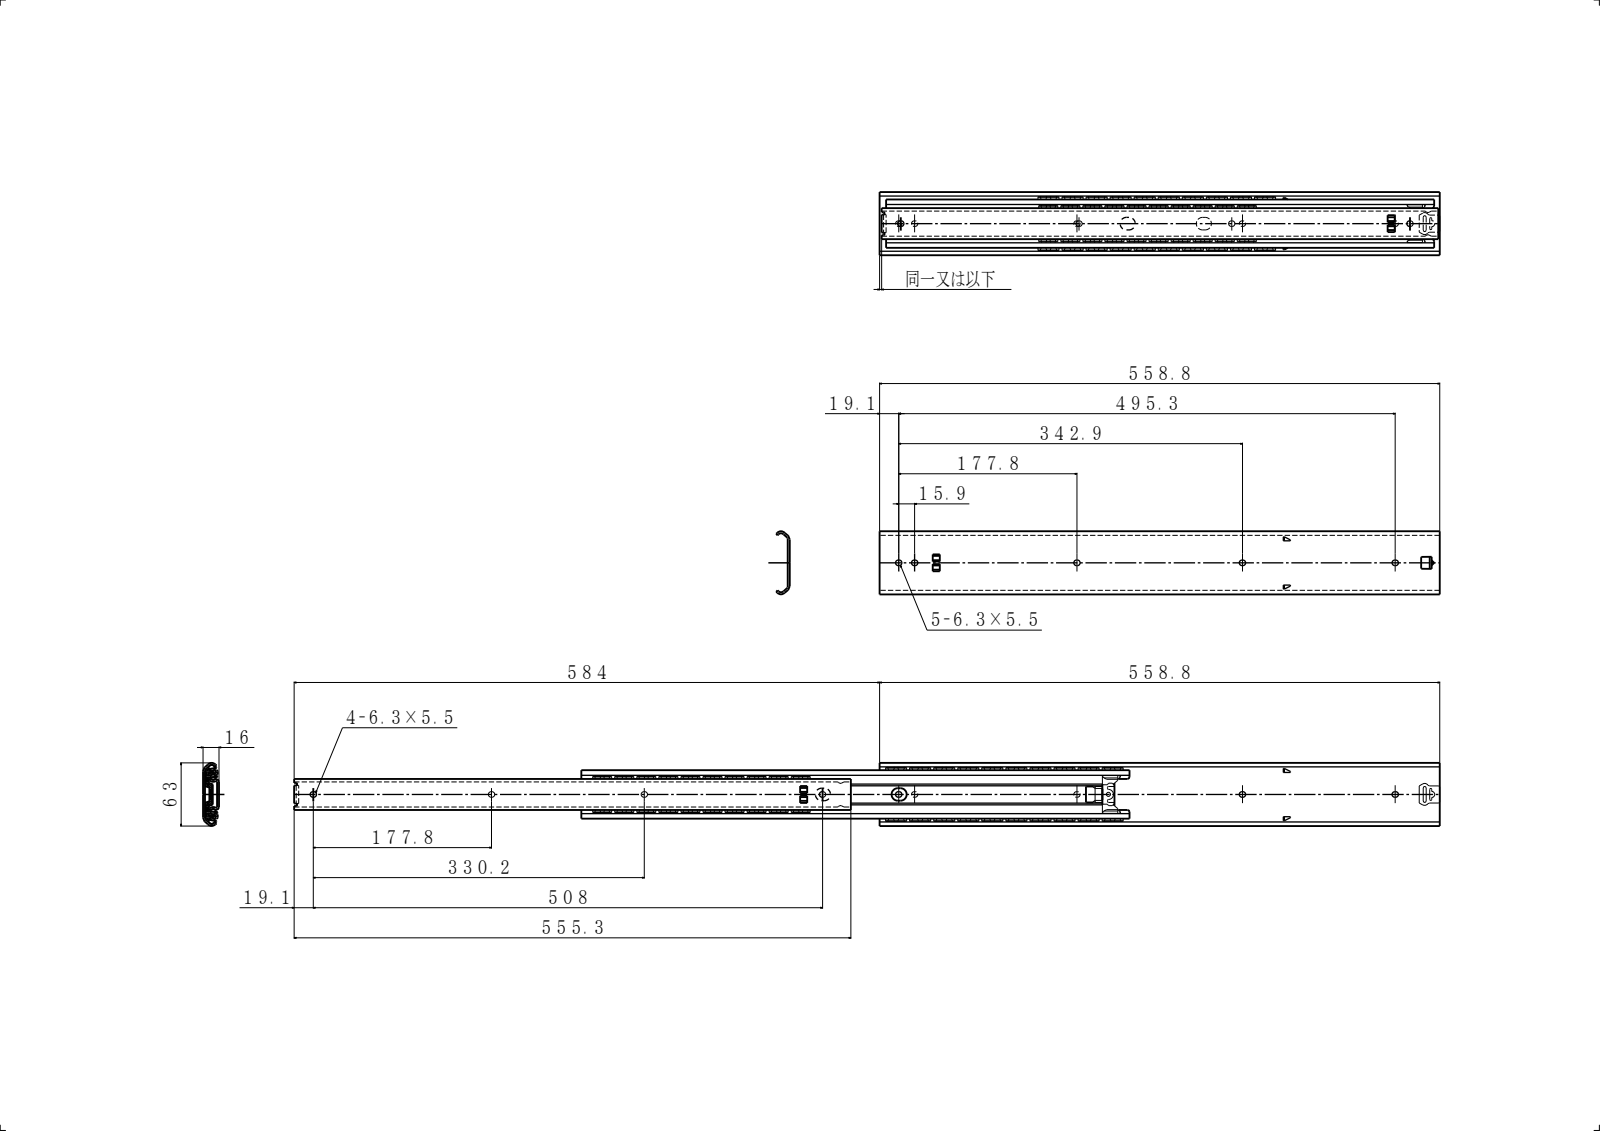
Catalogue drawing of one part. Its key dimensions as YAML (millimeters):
part_name: "PN68; C630-22; PN48B; PN161A (+5 more)"
step_written_by: "SolidWorks 2019 (CONFIG_CONTROL_DESIGN)"
units: millimeters
bodies: {solids: 10, faces: 634, planar: 392, cylindrical: 240, other: 2}
overall_size: [1143.34, 63, 16]
volume: 222464
surface_area: 252664
round_holes:
  - {diameter: 5.4, count: 1}
round_bosses_or_shafts:
  - {diameter: 5, count: 1}
partial_cylinders:
  - {radius: 1, count: 22}
  - {radius: 0.5, count: 20}
  - {radius: 2.75, count: 18}
  - {radius: 2, count: 16}
  - {radius: 0.3, count: 12}
  - {radius: 1.2, count: 10}
  - {radius: 0.2, count: 8}
  - {radius: 1.6, count: 8}
face_to_face_distances: [2, 14, 1.56, 12, 16, 4.08, 1.3, 12.7, 2.86, 11.14]
